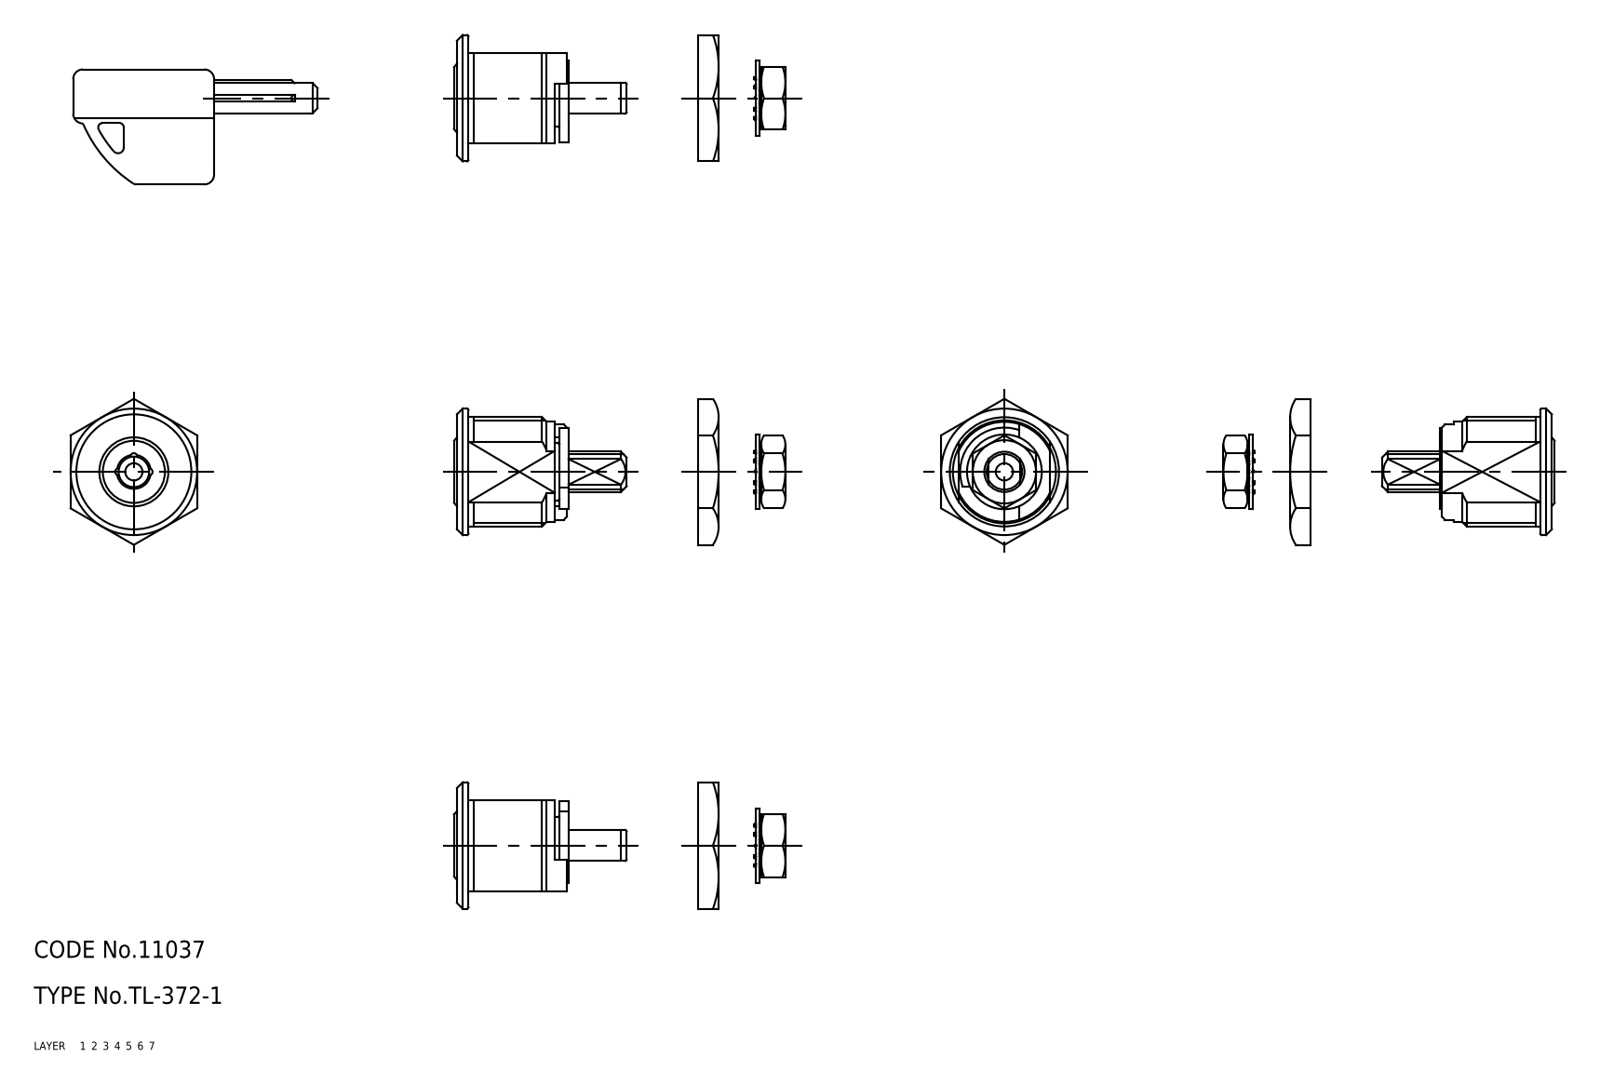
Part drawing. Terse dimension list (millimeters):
name: 67116549; 67116562; 67116575; 67116588 (+2 more)
written by: CADfix (AUTOMOTIVE_DESIGN)
unit: mm
bodies: 6 solids, 147 faces (0 planar, 0 cylindrical, 147 other)
size: 126.5 × 27.7 × 22
volume: 8 480 mm³; area: 6 191 mm²
